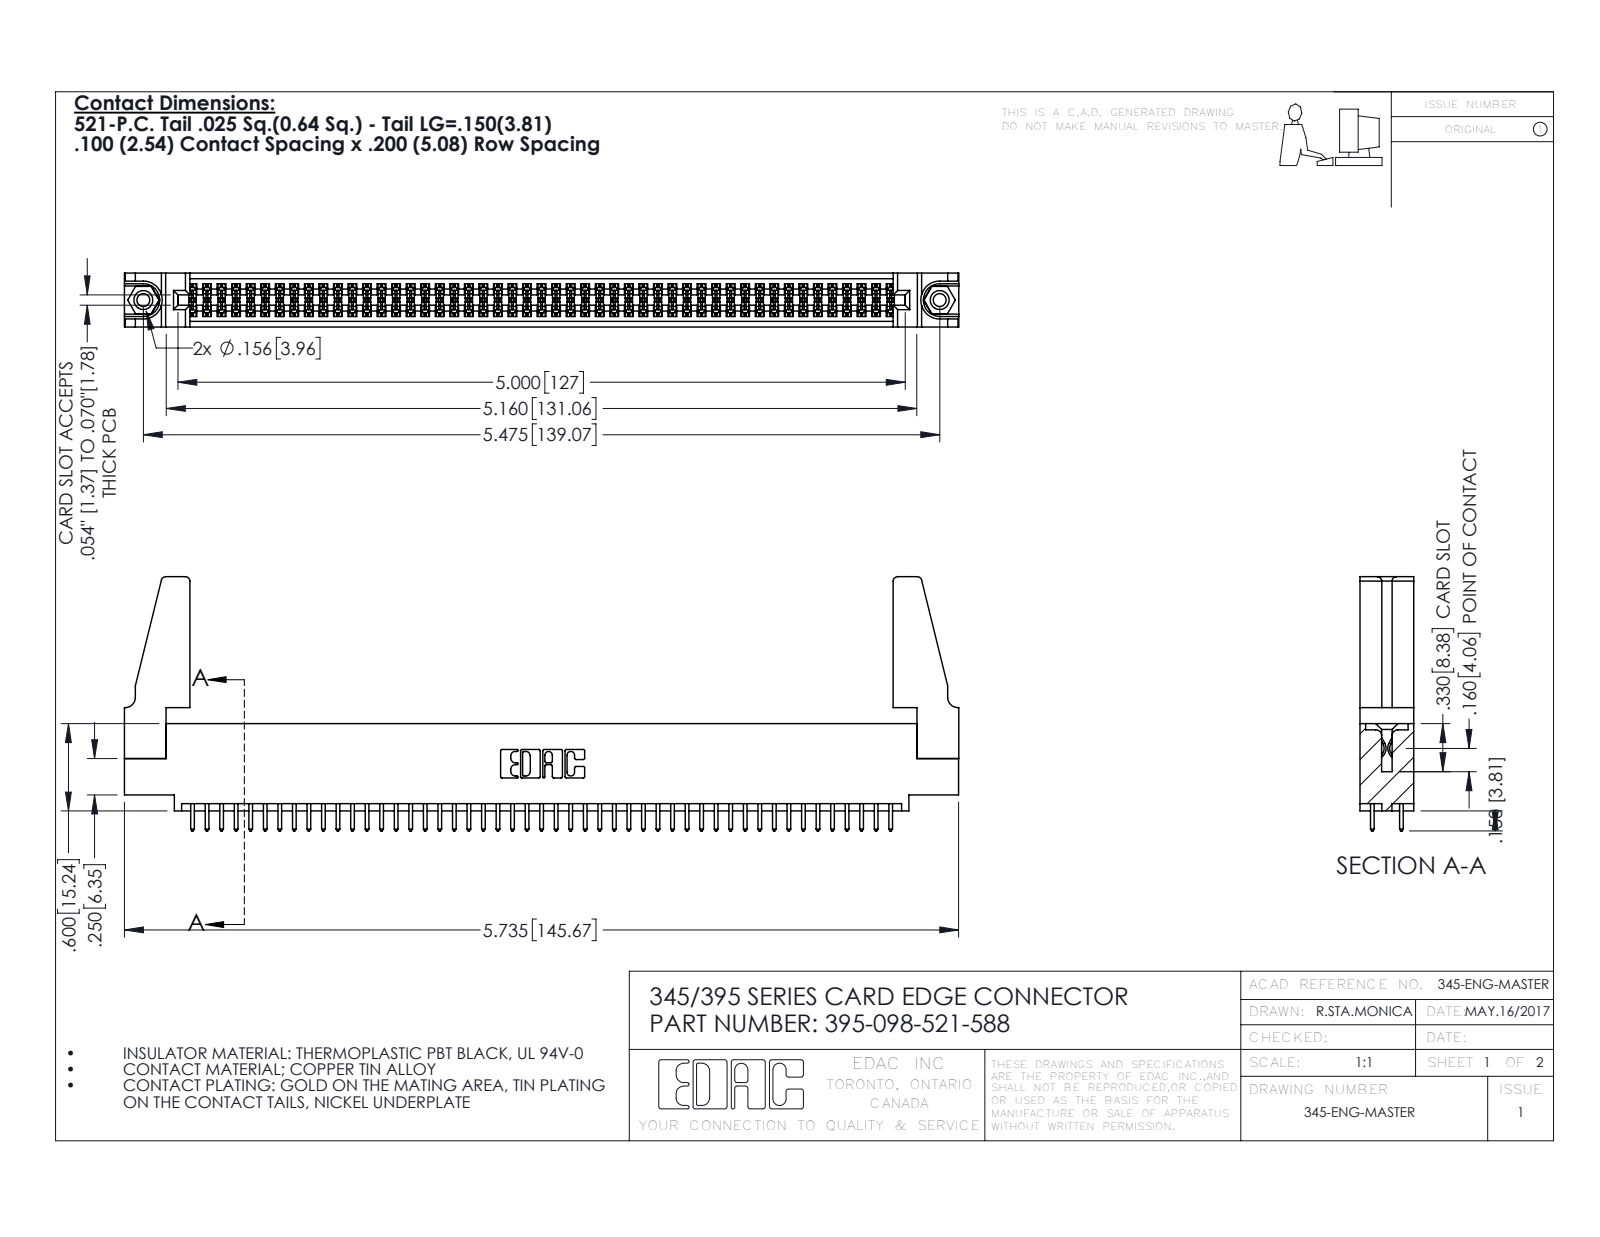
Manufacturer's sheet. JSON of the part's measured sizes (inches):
{"part_name": "345-250-001_345-250-001-102; 395-098-521-588; 345 Part_0.110 Offset - 0.156 Dia-TH; 345-220-078_345-220-088 (+1 more)", "step_written_by": "SolidWorks 2016 (CONFIG_CONTROL_DESIGN)", "units": "inches", "bodies": {"solids": 103, "faces": 5154, "planar": 3390, "cylindrical": 1748, "other": 16}, "overall_size": [5.736, 1.747, 0.37], "volume_in3": 1.059, "surface_area_in2": 37.11, "round_holes": [[0.089, 2], [0.125, 2], [0.156, 2], [0.064, 1]], "round_bosses_or_shafts": [[0.155, 2]], "partial_cylinders_radius": [[0.006, 147], [0.01, 98], [0.01, 22], [0.03, 8], [0.007, 6], [0.031, 6], [0.026, 3], [0.014, 2]], "face_to_face_distances": [0.072, 0.298, 0.37, 0.2, 0.098, 0.272, 0.025, 0.225, 0.175, 0.149], "hole_center_spacings": [0.27, 5.239, 5.475]}
